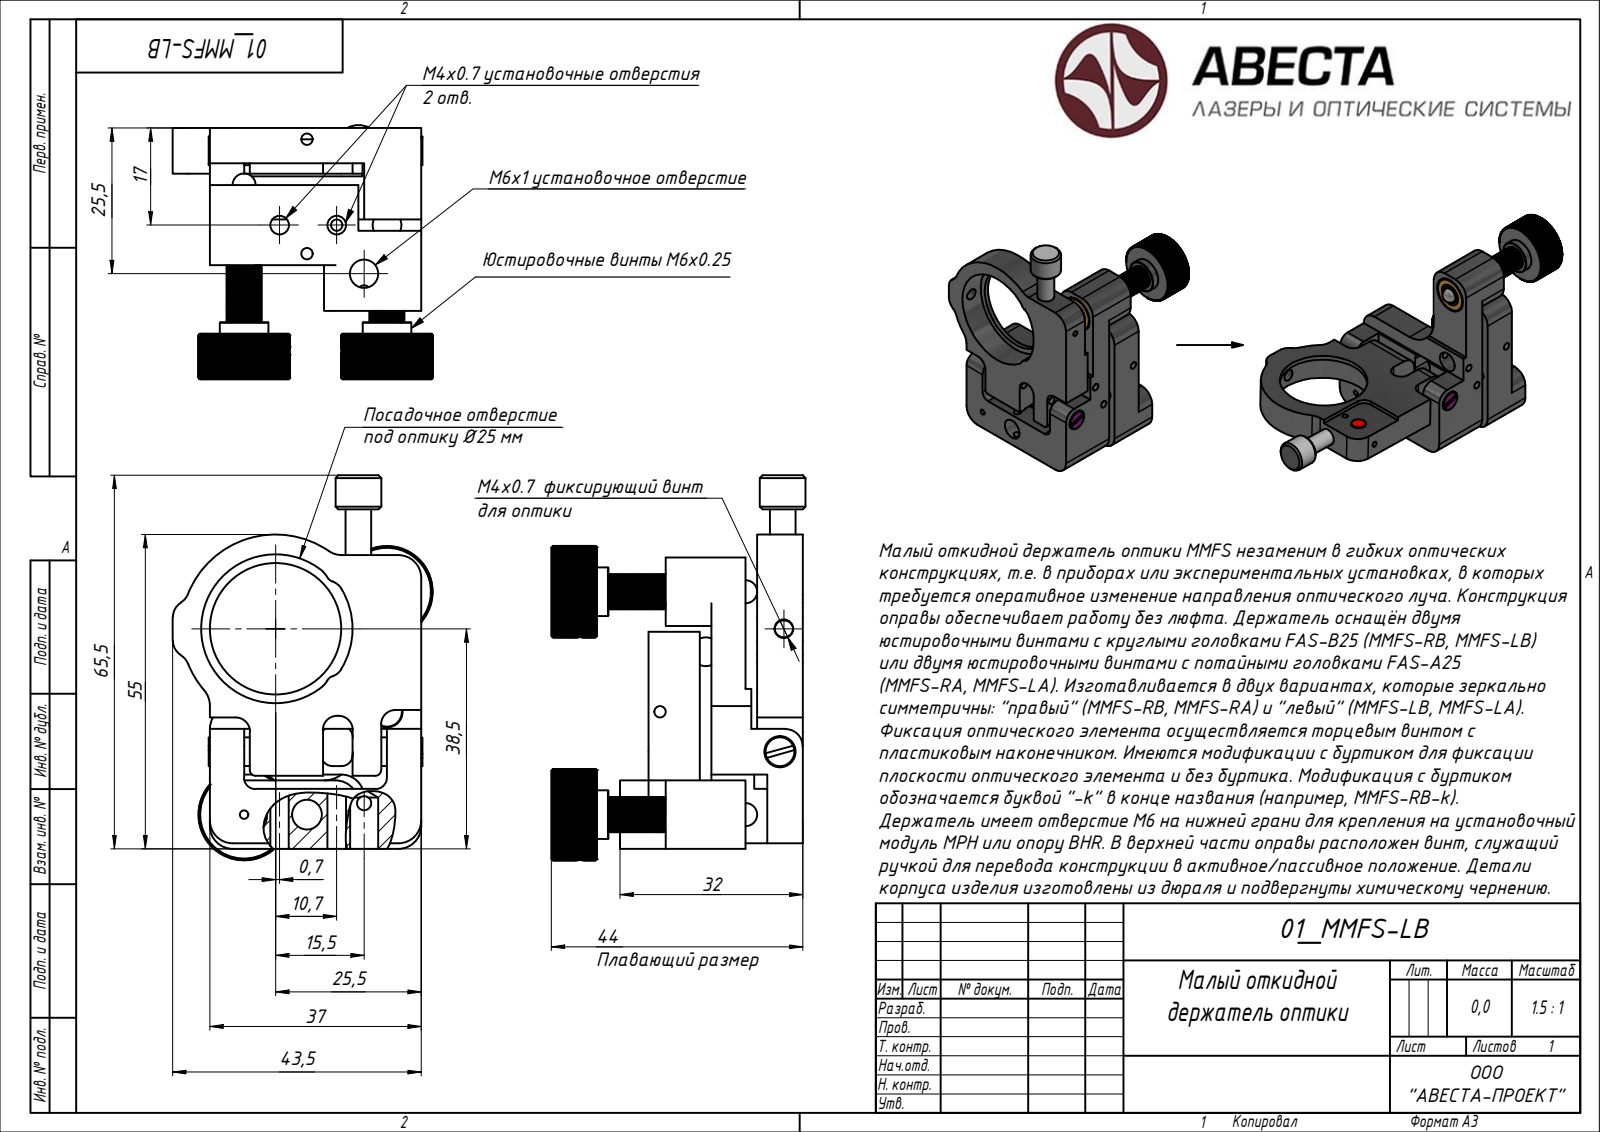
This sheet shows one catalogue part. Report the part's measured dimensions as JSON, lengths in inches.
{"step_written_by": "ST-DEVELOPER v15 (AUTOMOTIVE_DESIGN)", "units": "inches", "bodies": {"solids": 19, "faces": 779, "planar": 330, "cylindrical": 0, "other": 449}, "overall_size": [2.653, 1.791, 1.642], "volume_in3": 1.742, "surface_area_in2": 32.29, "face_to_face_distances": [0.315, 0.039, 0.079, 0.63, 0.354, 0.472, 0.236, 0.394, 0.433, 0.945]}
